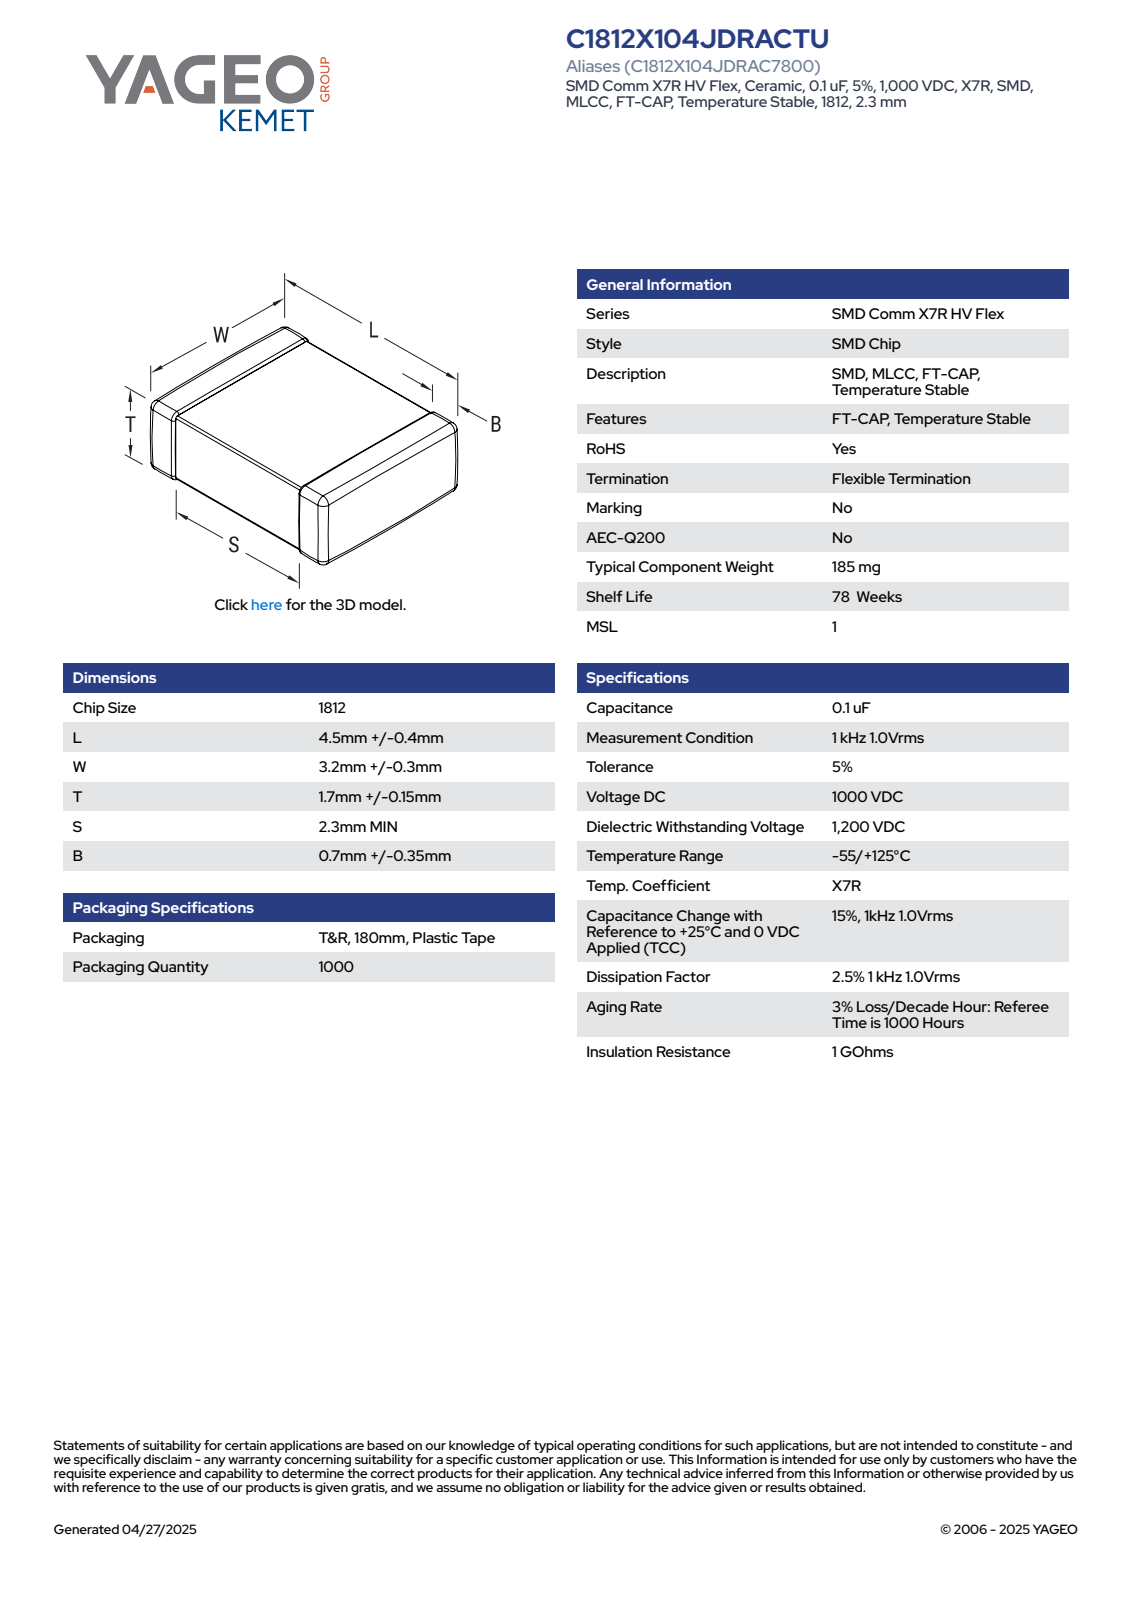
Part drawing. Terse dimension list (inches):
name: CCS_CCSTD_1812_L4.9W3.5T1.85B0.7
written by: SolidWorks 2021 (AUTOMOTIVE_DESIGN)
unit: in
bodies: 4 solids, 125 faces (71 planar, 38 cylindrical, 16 other)
size: 0.193 × 0.138 × 0.073
volume: 0.002 in³; area: 0.1 in²
face distances: 0.07, 0.067, 0.135, 0.073, 0.193, 0.132, 0.138, 0.02, 0.089, 0.084
